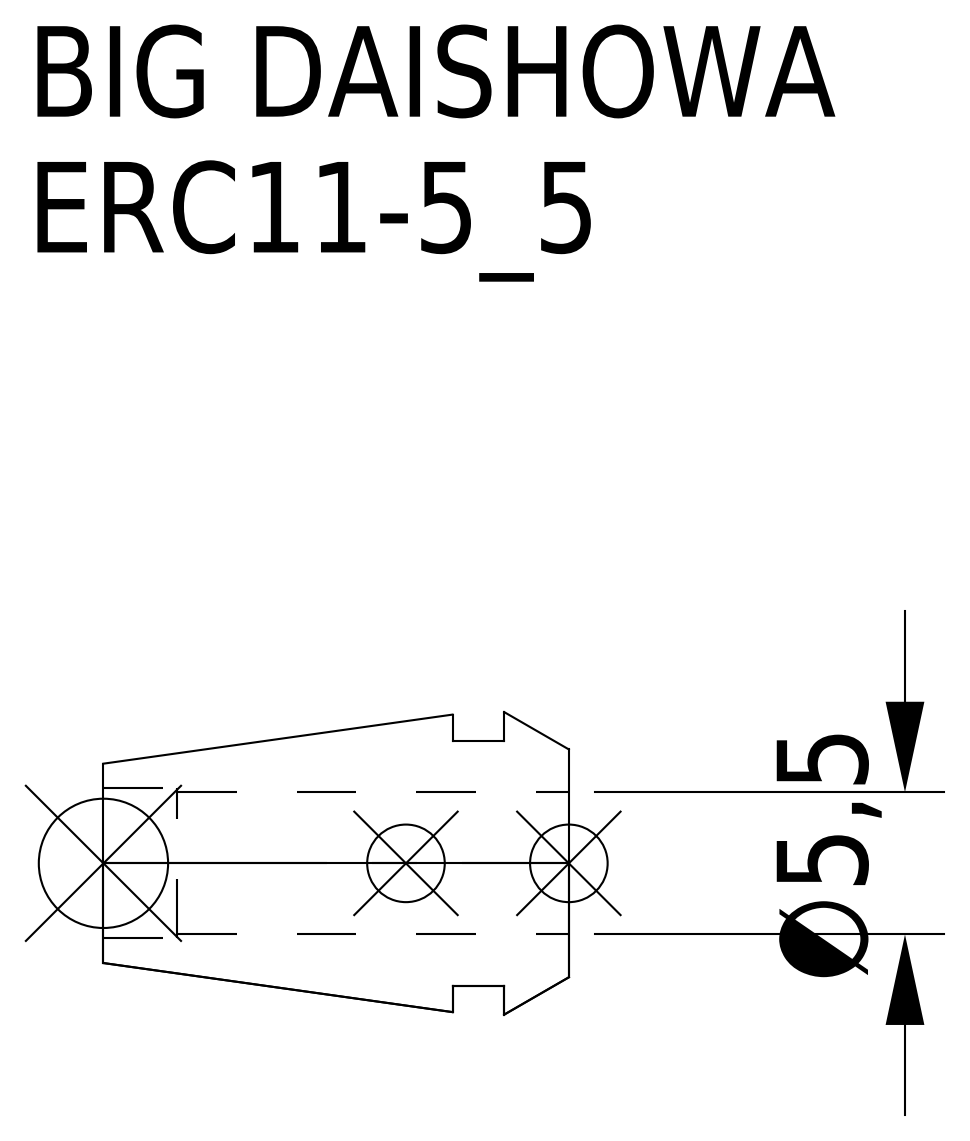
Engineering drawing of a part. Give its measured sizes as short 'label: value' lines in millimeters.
name: ERC11-5_5
written by: CREO PARAMETRIC BY PTC INC, 2016380 (AUTOMOTIVE_DESIGN)
unit: mm
bodies: 1 solid, 15 faces (5 planar, 6 cylindrical, 4 other)
size: 18 × 11.7 × 11.7
volume: 906 mm³; area: 1 008 mm²
holes: 1× ⌀5.5, 1× ⌀5.8
bosses: 1× ⌀9.5
face distances: 2.5, 4.5, 2, 18, 15.5, 13.5, 15.14, 12.64, 10.64, 2.86
